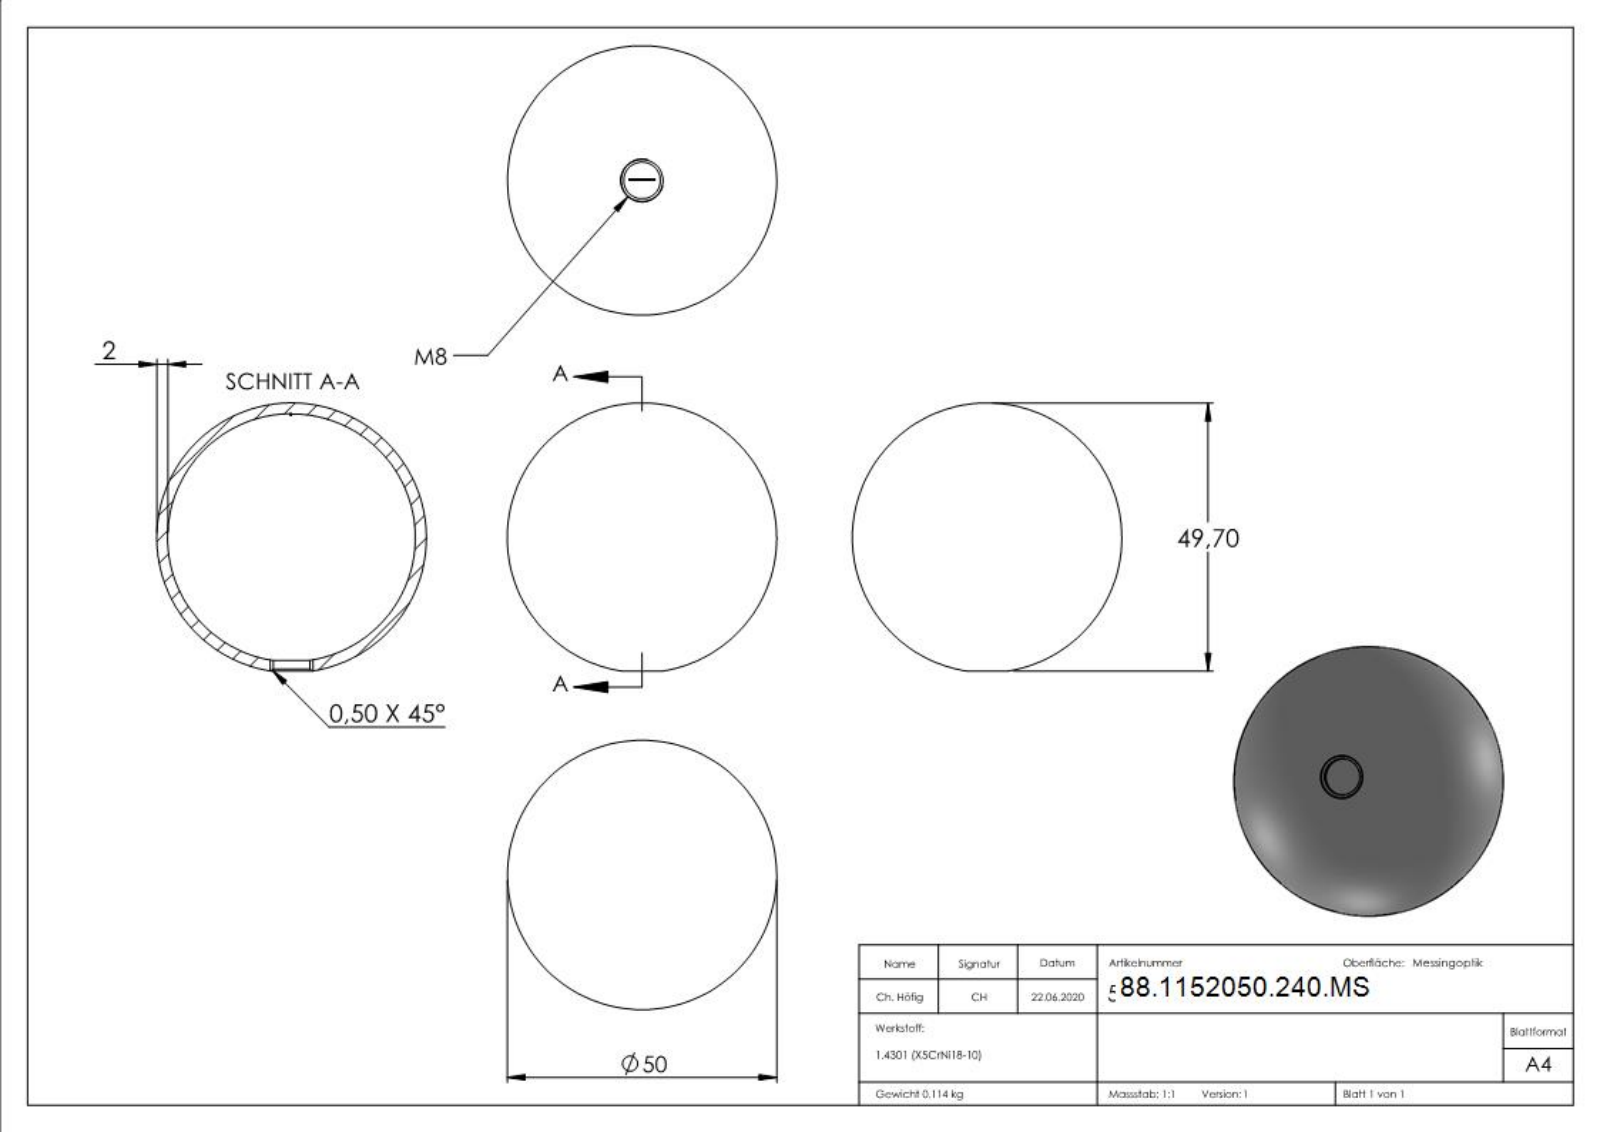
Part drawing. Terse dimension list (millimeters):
name: 52050-240-MS
written by: SolidWorks 2015 (CONFIG_CONTROL_DESIGN)
unit: mm
bodies: 1 solid, 263 faces (114 planar, 1 cylindrical, 148 other)
size: 50 × 50 × 49.7
volume: 14 409 mm³; area: 14 468 mm²
holes: 1× ⌀6.8
face distances: 0.31, 0.68, 0.74, 3.32, 0.76, 0.65, 0.99, 0.45, 0.7, 0.77
